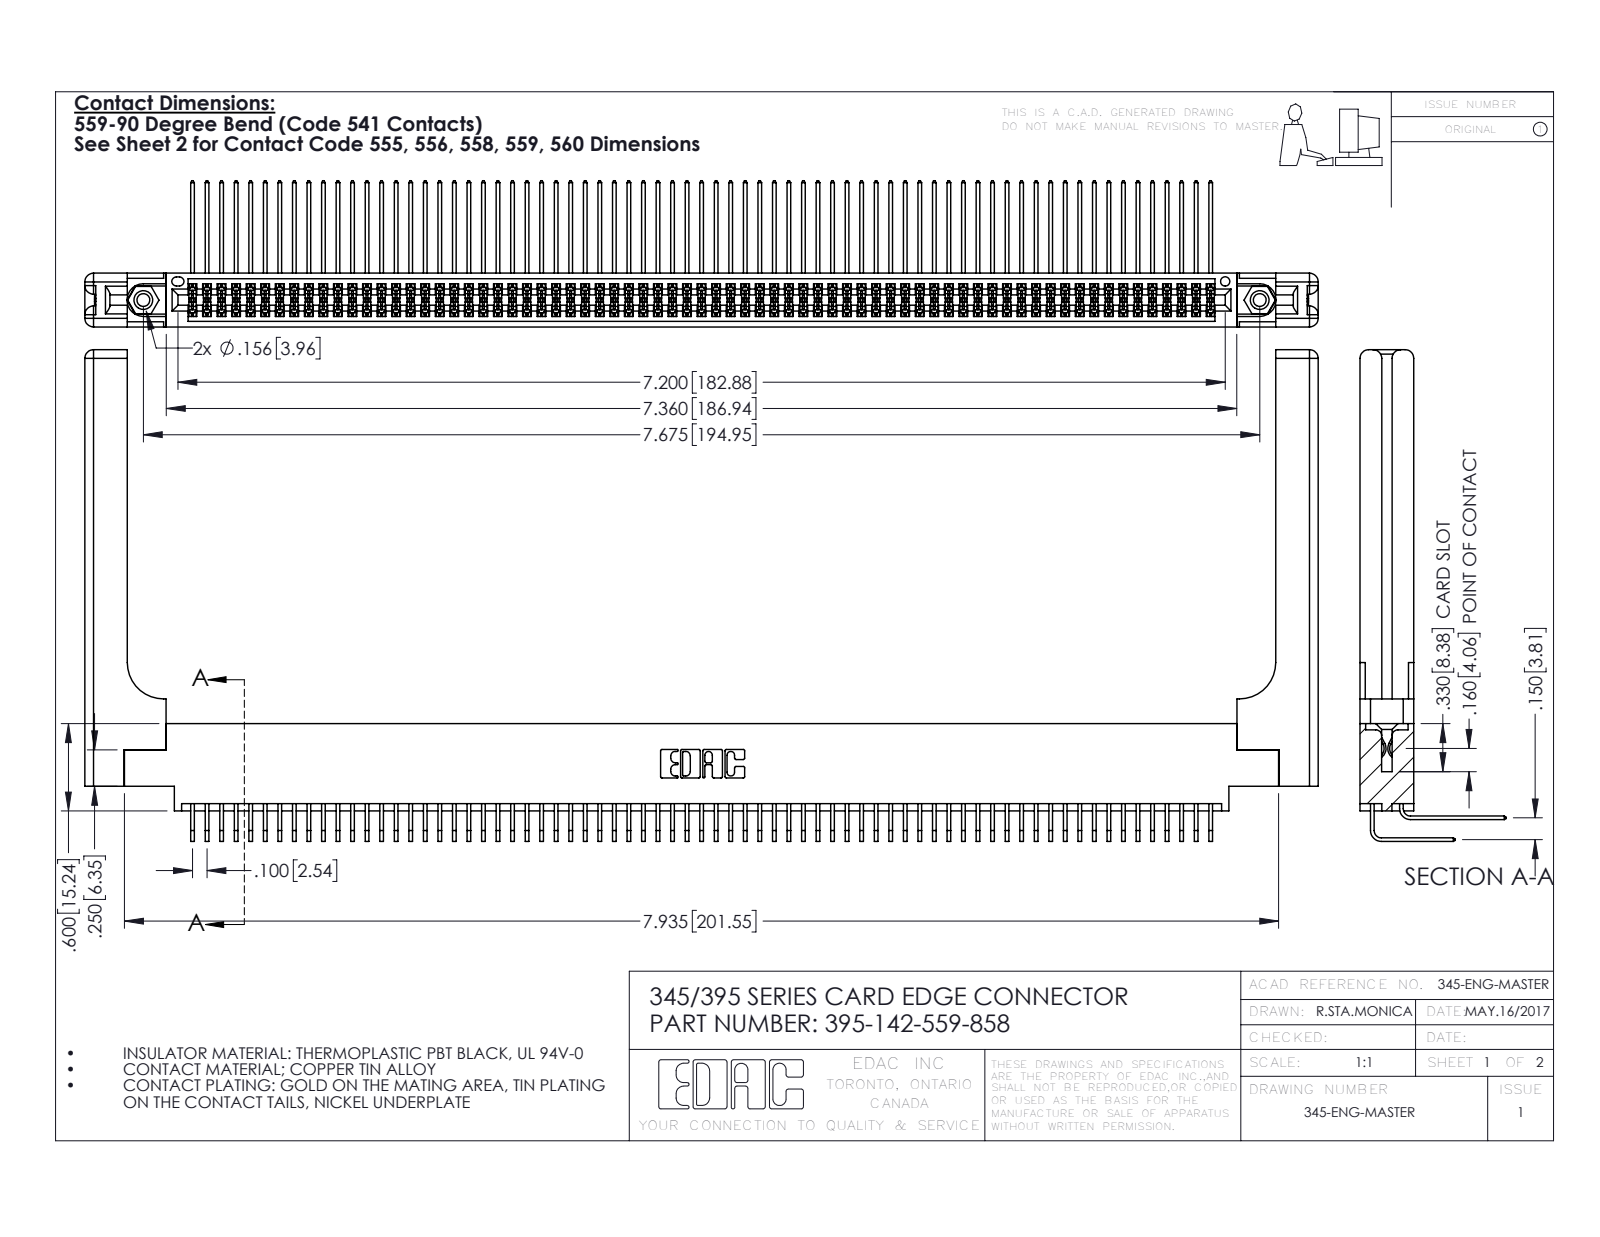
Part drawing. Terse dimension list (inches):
name: 345-220-058_345-220-058; 345 Part_0.170 Offset - 0.156 Dia-TH; 395-142-559-858; 345-292-001_558 559 Tail - 1 (+2 more)
written by: SolidWorks 2016 (CONFIG_CONTROL_DESIGN)
unit: in
bodies: 147 solids, 7770 faces (5202 planar, 2508 cylindrical, 60 other)
size: 8.479 × 3.379 × 1.005
volume: 1.853 in³; area: 65.07 in²
holes: 2× ⌀0.089, 2× ⌀0.125, 2× ⌀0.156, 1× ⌀0.064
bosses: 2× ⌀0.155
rounds: 284× R0.006, 22× R0.01, 16× R0.06, 6× R0.007, 6× R0.031, 3× R0.026, 2× R0.014, 2× R0.019
face distances: 0.072, 0.298, 0.37, 0.098, 0.272, 0.025, 0.2, 0.225, 0.175, 0.15
hole spacings: 0.27, 7.439, 7.675
